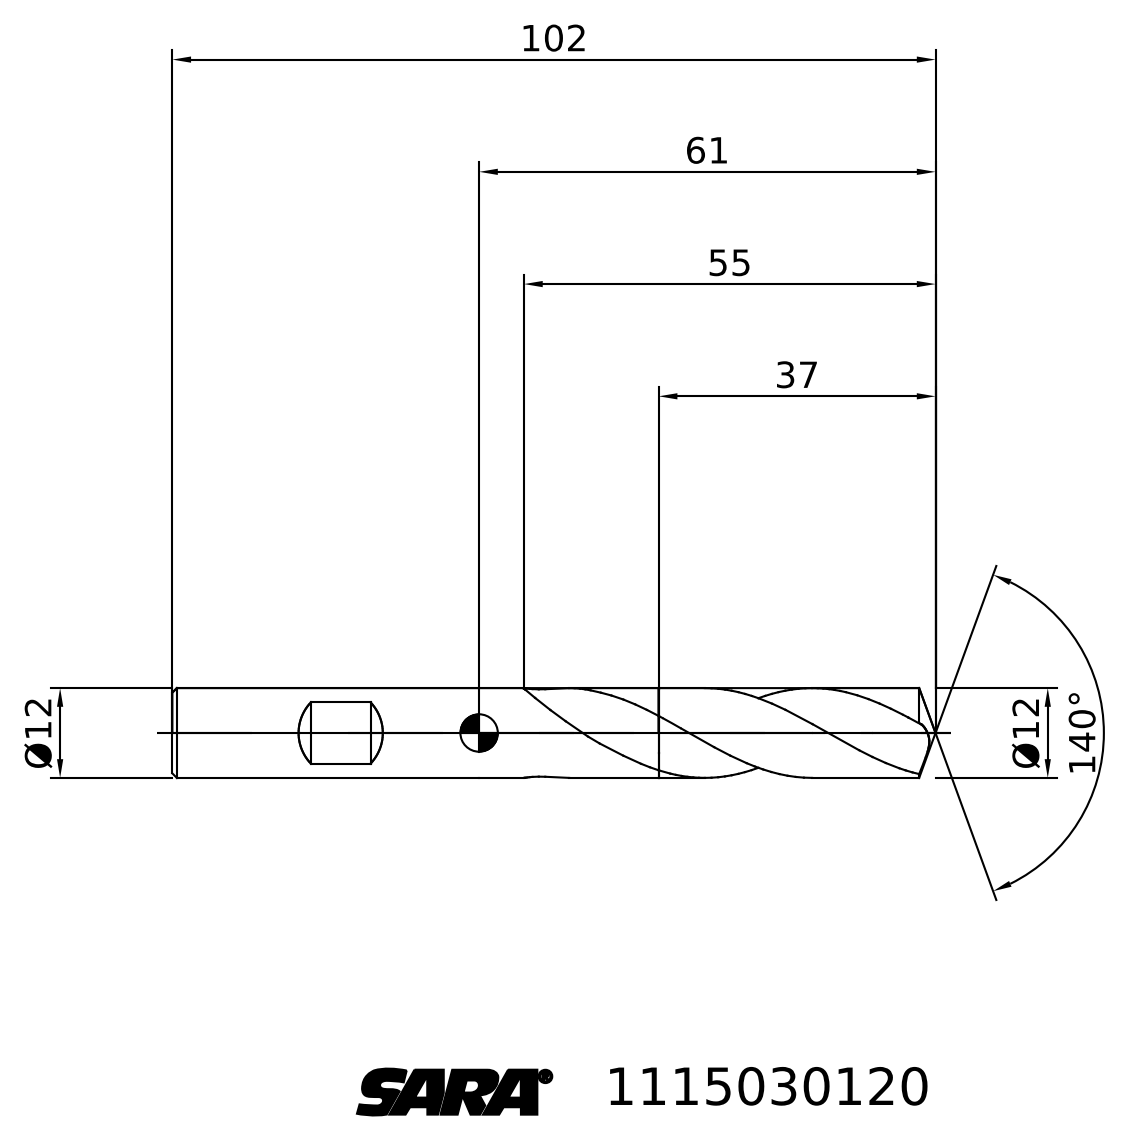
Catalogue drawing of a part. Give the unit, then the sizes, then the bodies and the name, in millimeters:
Units: millimetres
Overall size (bounding box): 102 × 16.14 × 12
Main face-to-face distances: 65
Volume: 9 351 mm³ · Surface area: 4 279 mm²
Bodies: 2 solids, 29 faces (6 planar, 0 cylindrical, 23 other)
STEP written by: TDM (AUTOMOTIVE_DESIGN)
